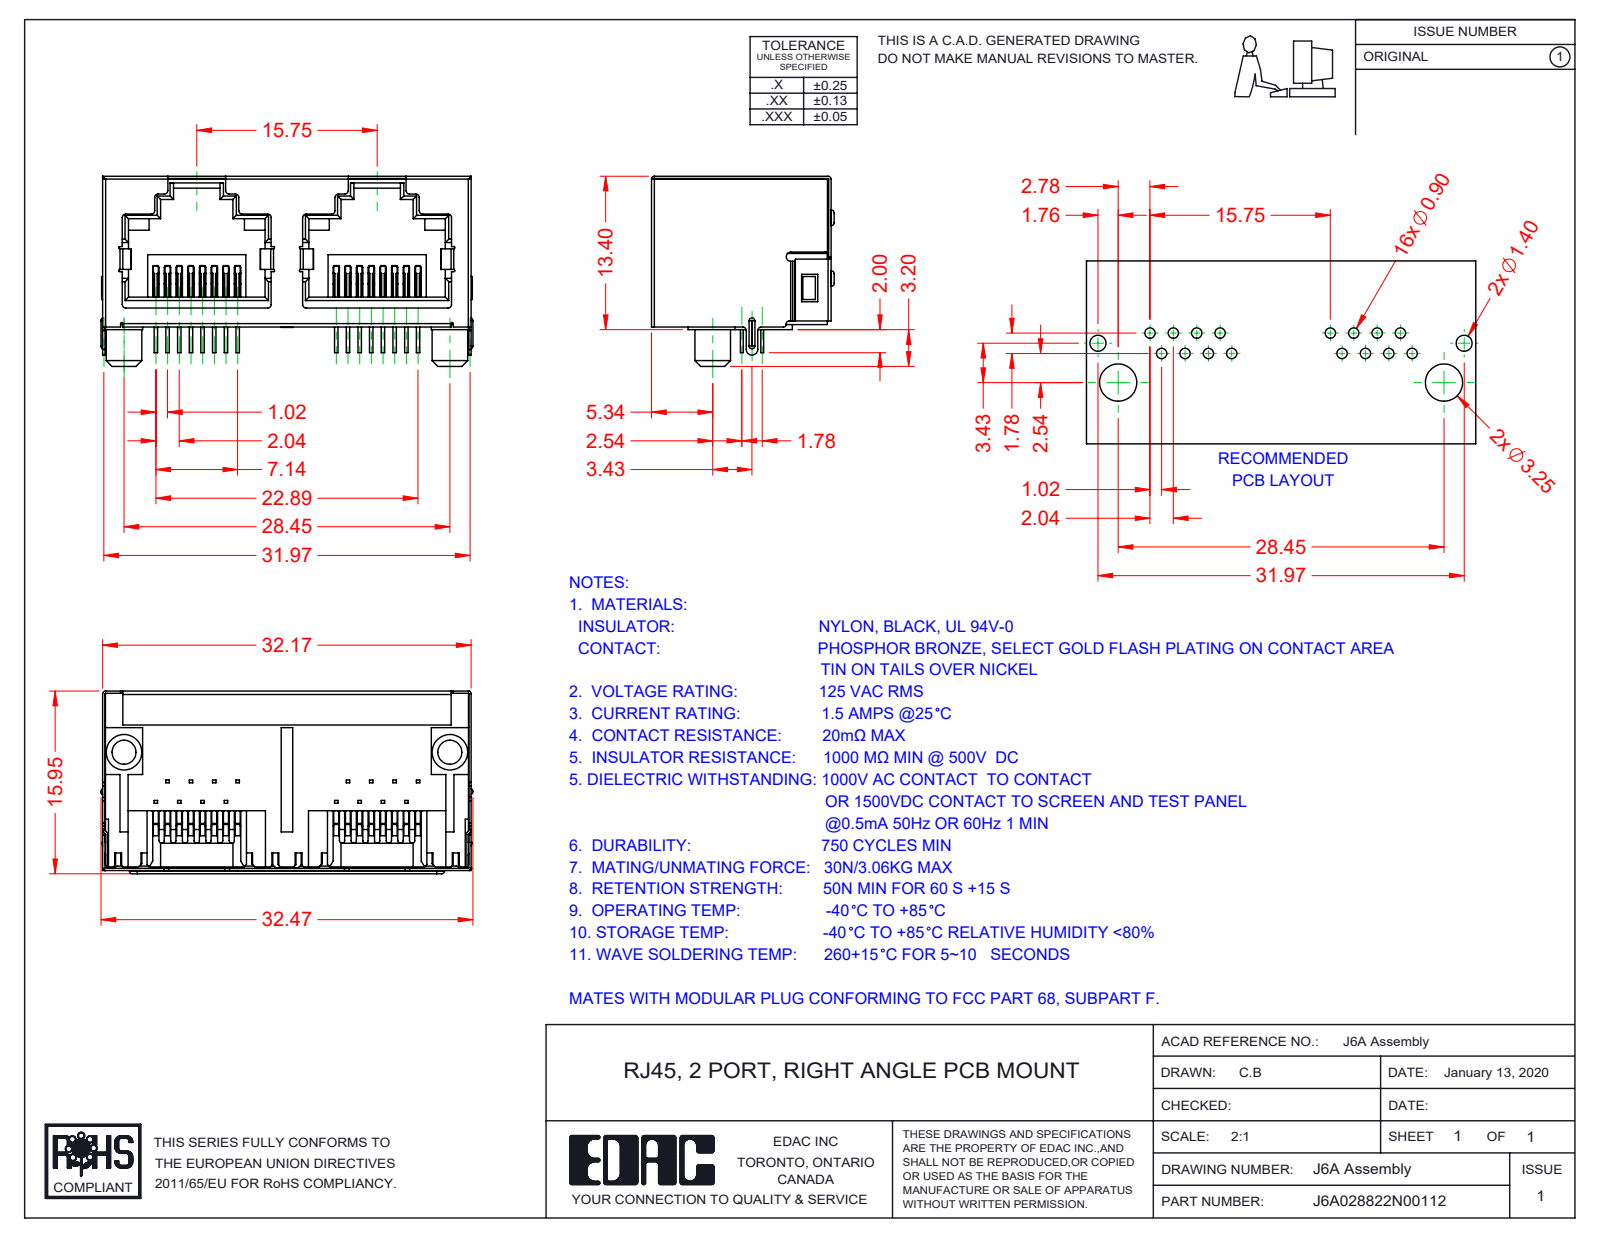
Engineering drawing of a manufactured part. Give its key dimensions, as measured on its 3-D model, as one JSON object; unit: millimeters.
{"part_name": "6A Contacts; 6A Shield; J6A028822N00112; 6A Insulator", "step_written_by": "SolidWorks 2016 (CONFIG_CONTROL_DESIGN)", "units": "millimeters", "bodies": {"solids": 18, "faces": 1823, "planar": 1380, "cylindrical": 415, "other": 28}, "overall_size": [32.47, 16.6, 15.95], "volume_mm3": 2964, "surface_area_mm2": 8172, "round_bosses_or_shafts": [[3.1, 2]], "partial_cylinders_radius": [[0.1, 44], [0.3, 44], [0.25, 23], [0.2, 16], [0.23, 14], [0.21, 4], [0.47, 4], [0.68, 4]], "face_to_face_distances": [15.75, 0.85, 31.97, 12.95, 12.7, 12.75, 15.47, 10.55, 2, 2.4]}
